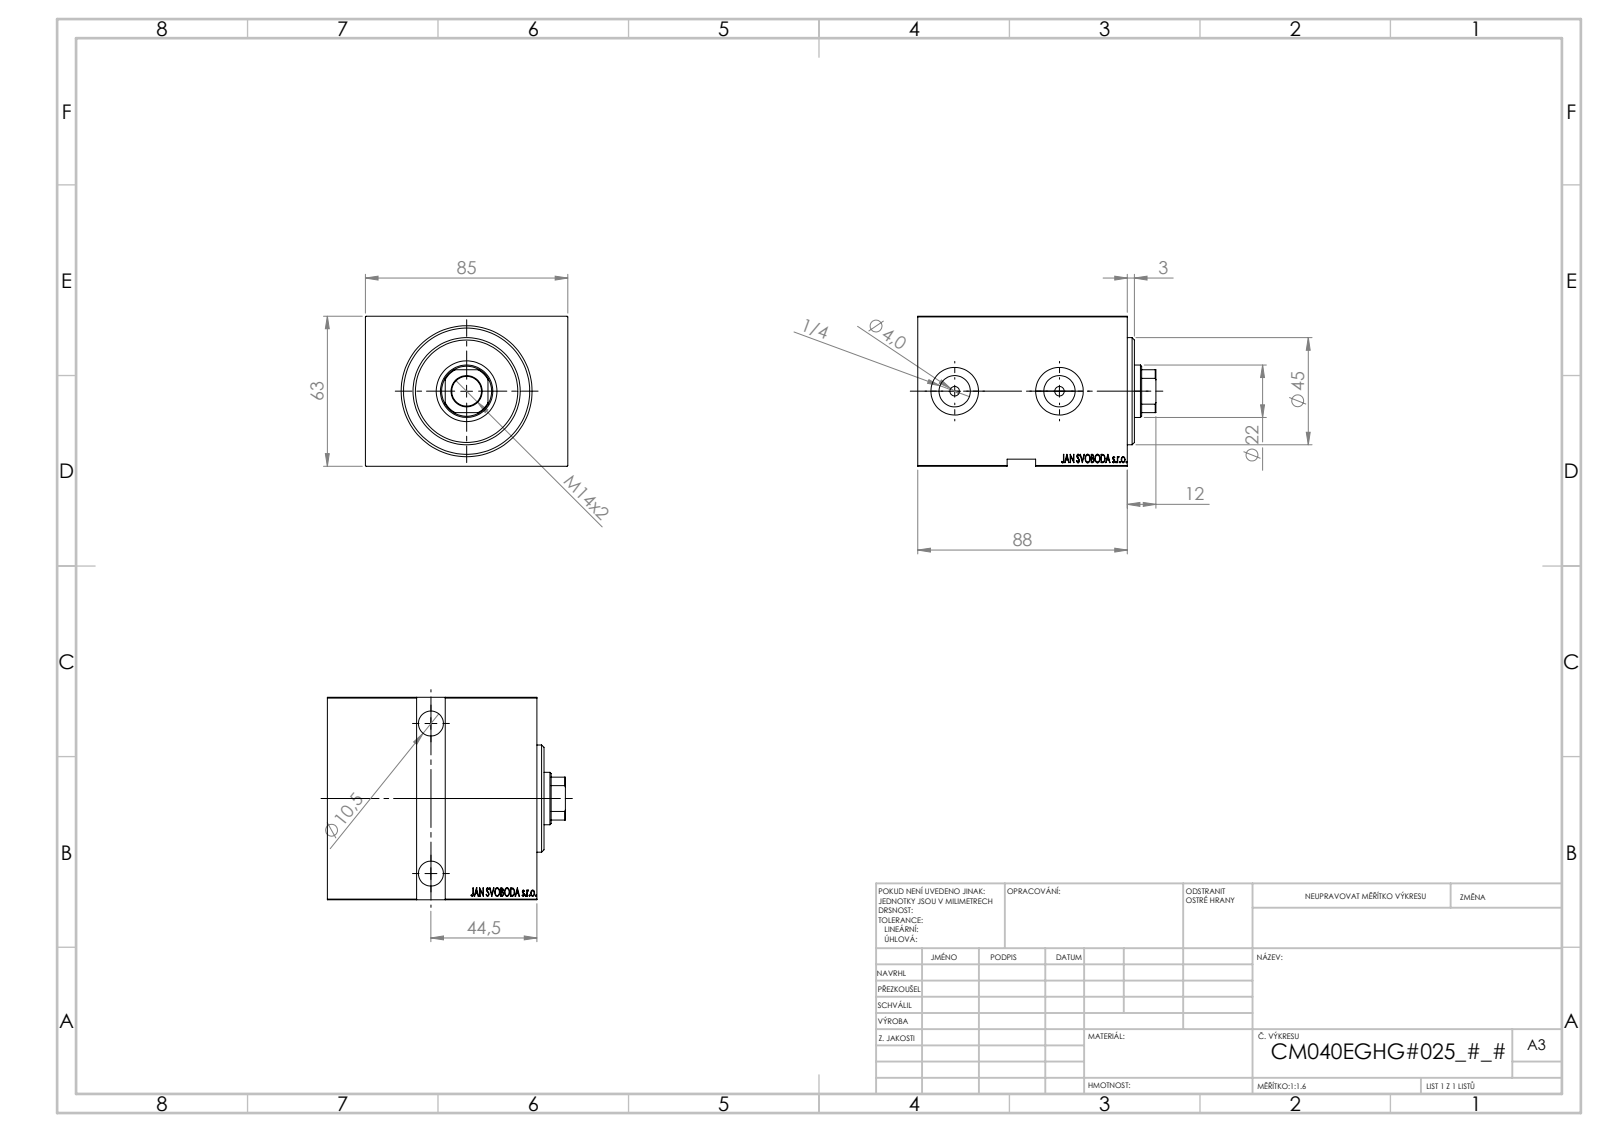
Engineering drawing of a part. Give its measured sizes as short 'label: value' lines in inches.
name: V450CM_E_VCP; V450CM_E_Body; V450CM_VC_B
written by: SolidWorks 2019 (CONFIG_CONTROL_DESIGN)
unit: in
bodies: 3 solids, 846 faces (408 planar, 44 cylindrical, 394 other)
size: 3.937 × 3.346 × 2.48
volume: 26.73 in³; area: 111.1 in²
holes: 2× ⌀0.157, 2× ⌀0.413, 2× ⌀0.518, 2× ⌀0.65, 2× ⌀0.787, 1× ⌀0.492, 1× ⌀0.866, 1× ⌀1.004, 1× ⌀1.575, 1× ⌀2.087
bosses: 1× ⌀1.772, 1× ⌀1.654
rounds: 1× R0.413
face distances: 2.48, 3.346, 3.465, 0.472, 2.992, 0.118, 0.197, 3.268, 2.795, 1.575
hole spacings: 1.732, 2.48
